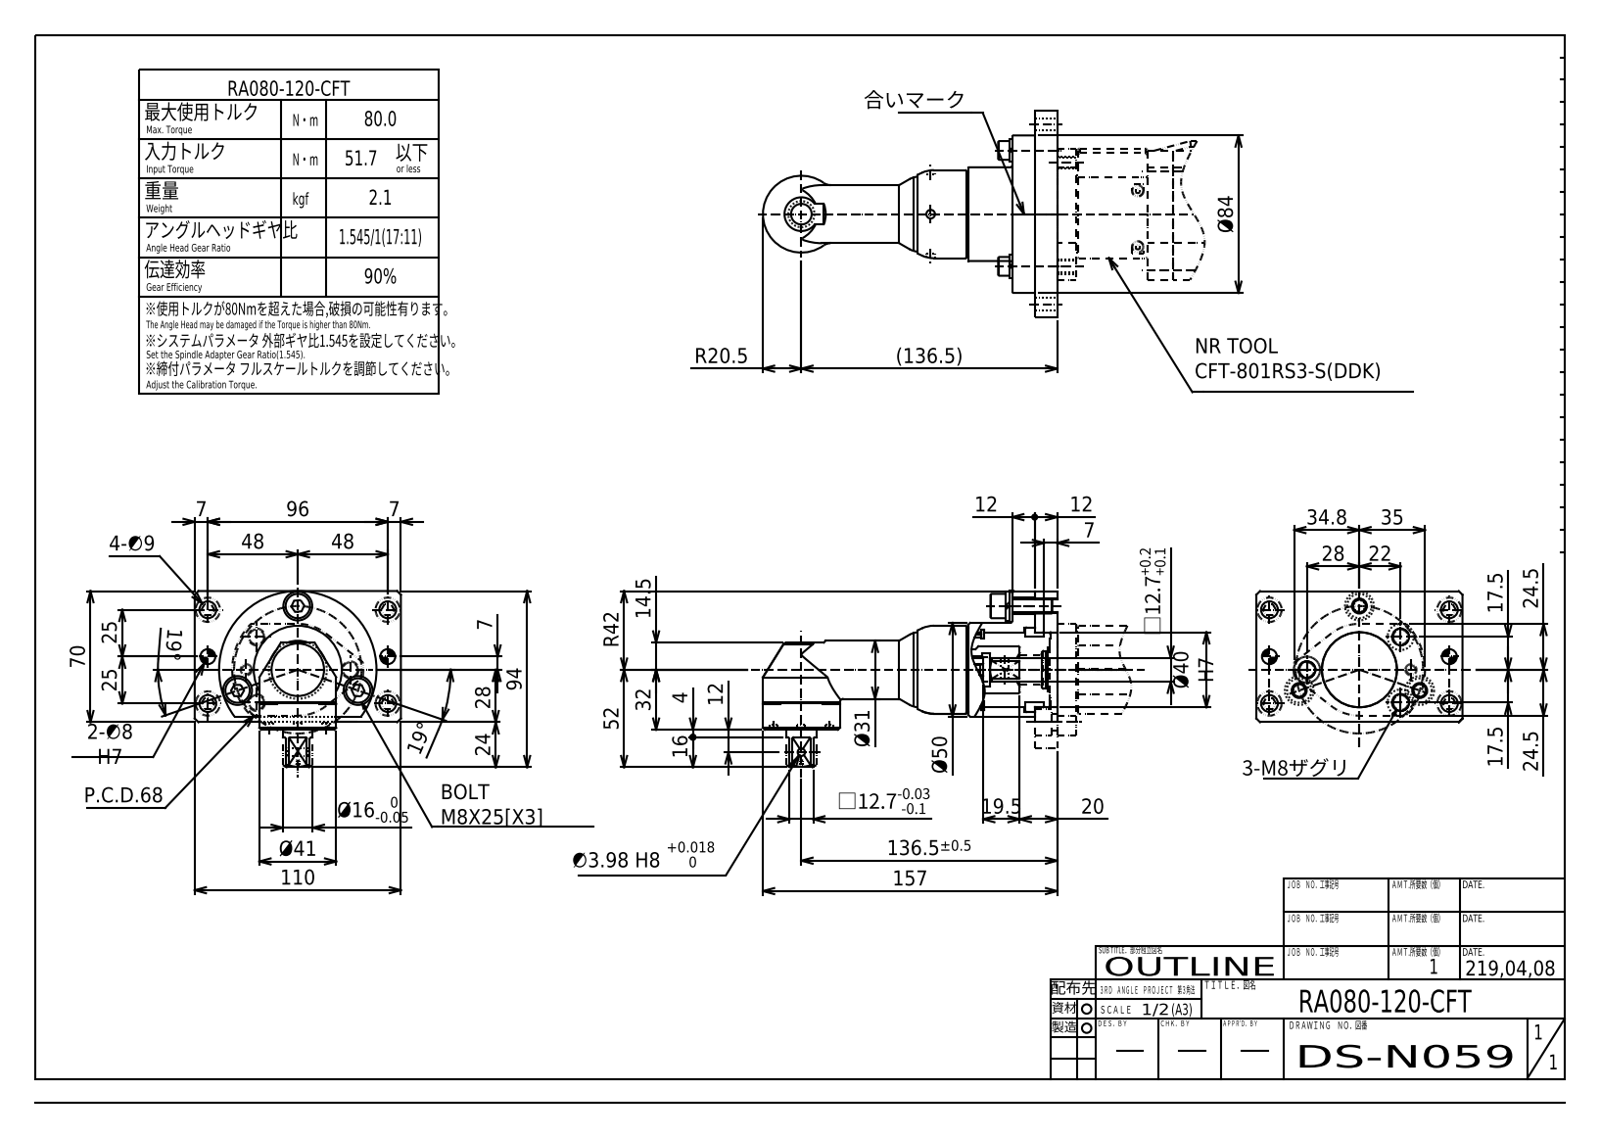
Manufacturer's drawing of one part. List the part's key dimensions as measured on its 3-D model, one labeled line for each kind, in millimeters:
Part name (STEP PRODUCT): RA080-120-CFT(DS-N059)
STEP written by: Autodesk Inventor 2019 (AUTOMOTIVE_DESIGN)
Units: millimetres
Bodies: 1 solid, 247 faces (120 planar, 83 cylindrical, 44 other)
Overall size (bounding box): 157 × 110 × 94.5
Volume: 285 565 mm³ · Surface area: 59 422 mm²
Round holes (diameter × count): ⌀9 ×7, ⌀4.1 ×4, ⌀4.92 ×3, ⌀8.2 ×3, ⌀8.4 ×3, ⌀14 ×3, ⌀4.6 ×2, ⌀8 ×2, ⌀1.6 ×1, ⌀3.98 ×1, ⌀11 ×1, ⌀16.6 ×1
Round bosses / shafts (diameter × count): ⌀17 ×3, ⌀15.4 ×3, ⌀13 ×3, ⌀8 ×3, ⌀50 ×1, ⌀47 ×1, ⌀45 ×1, ⌀41 ×1
Partial cylindrical surfaces — rounded edges, fillets, slot ends (radius × count): R1 ×8, R4.2 ×6, R29.8 ×1, R38.2 ×1, R42 ×1
Main face-to-face distances: 12, 24, 7, 4, 3, 70, 17, 74, 67, 110
Hole centre spacings: 15, 21.21, 25, 99.2, 34, 96, 17.3, 24.04
